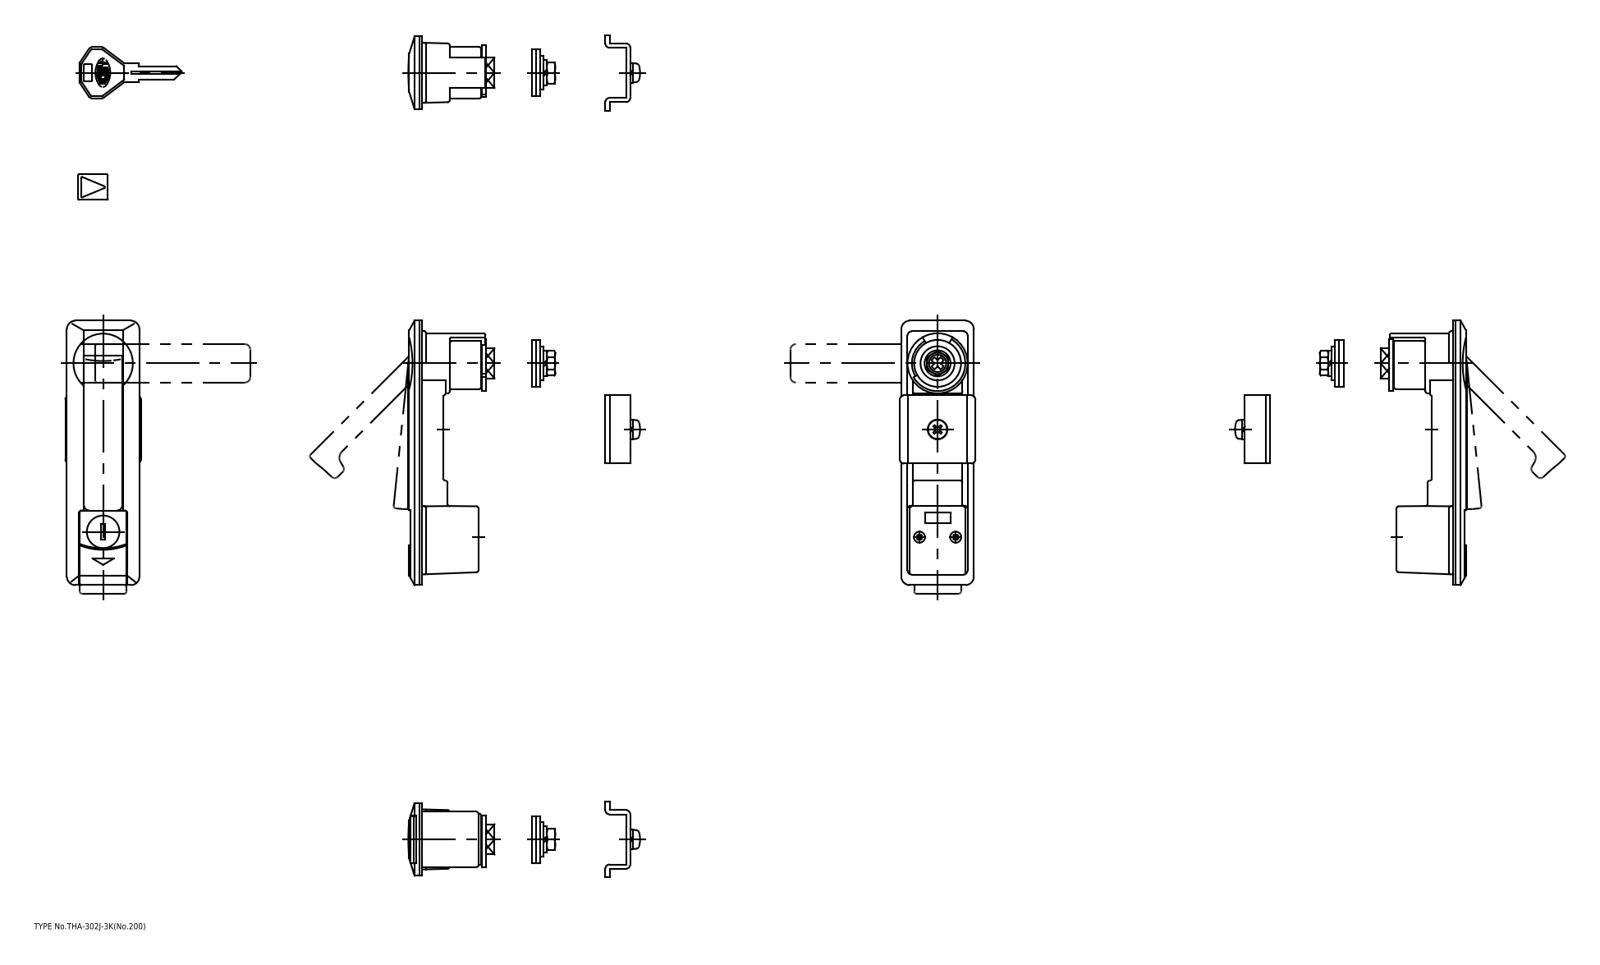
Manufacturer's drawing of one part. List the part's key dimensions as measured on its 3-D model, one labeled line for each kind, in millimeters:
Part name (STEP PRODUCT): key; lock; handle; washer_B (+8 more)
STEP written by: CADfix (AUTOMOTIVE_DESIGN)
Units: millimetres
Bodies: 13 solids, 492 faces (0 planar, 0 cylindrical, 492 other)
Overall size (bounding box): 124 × 116.75 × 35.5
Volume: 55 965 mm³ · Surface area: 47 774 mm²
